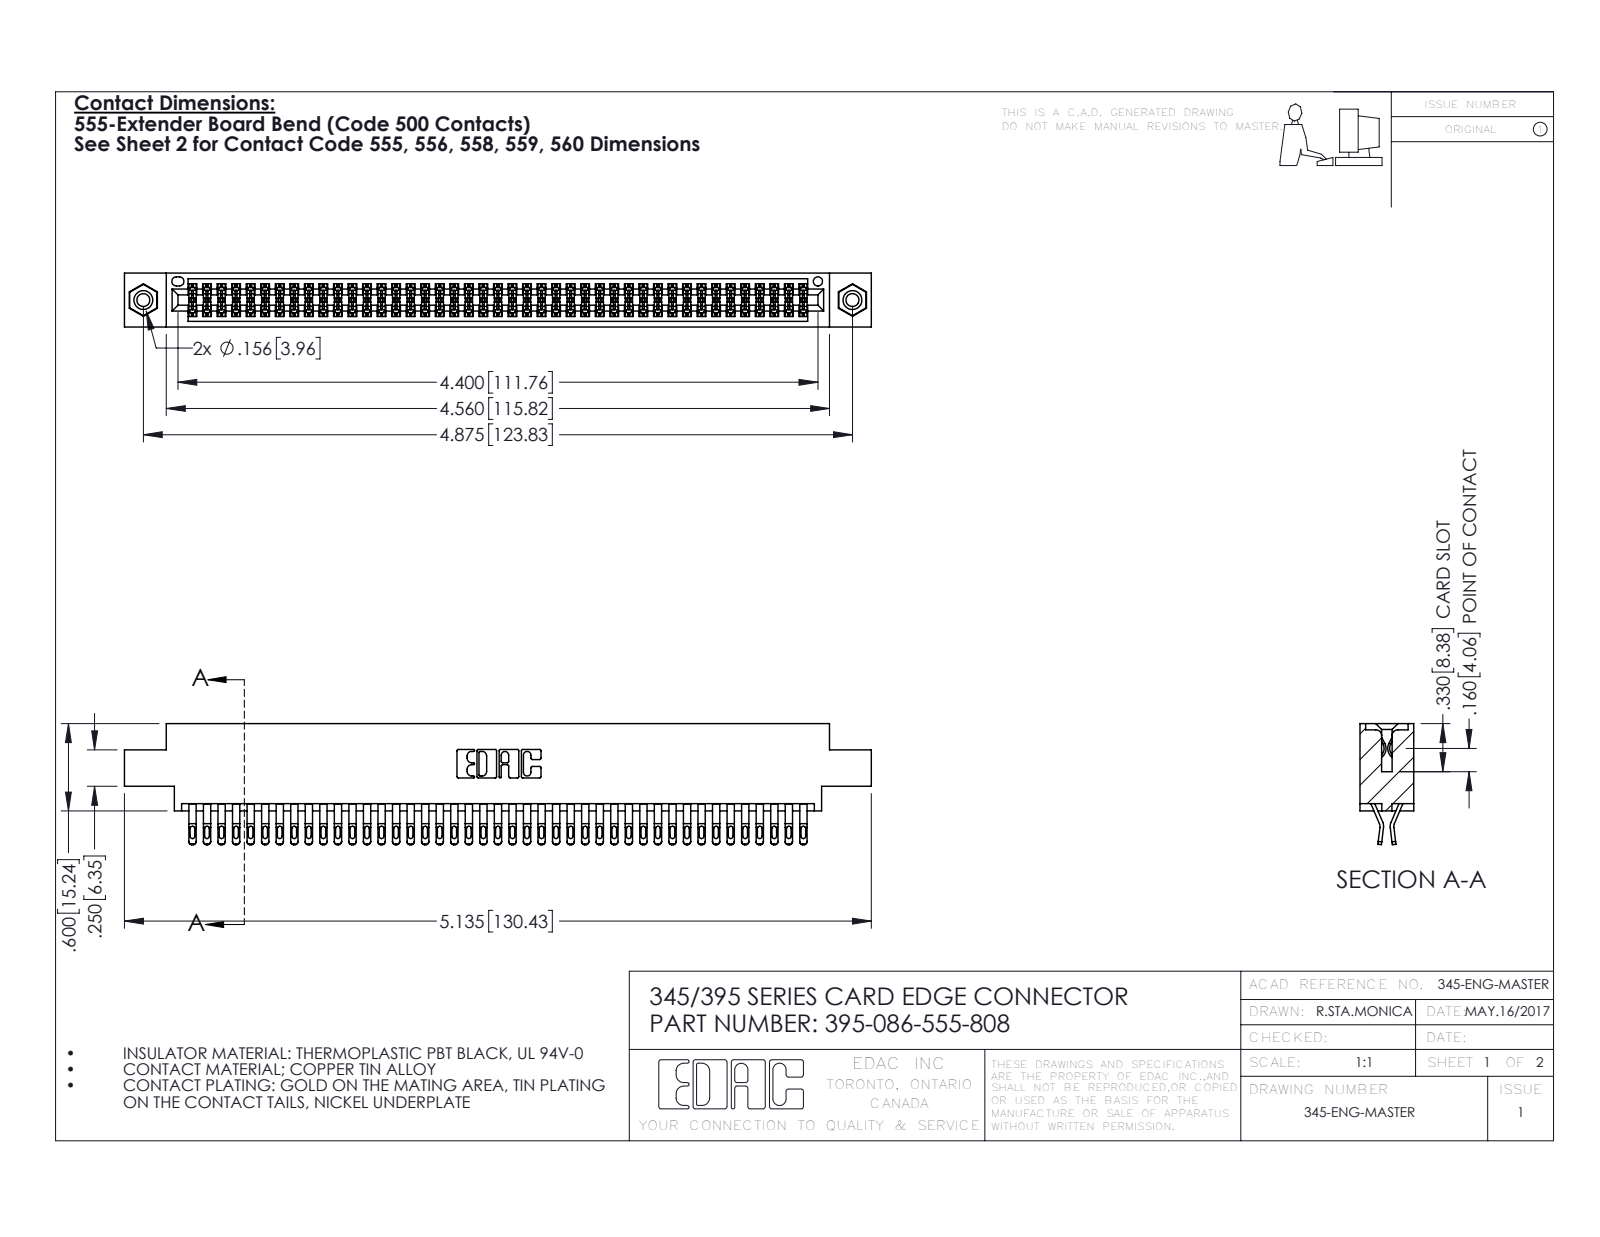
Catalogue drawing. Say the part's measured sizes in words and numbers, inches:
The part is named "395-086-555-808; 345-292-001_555 Tail; 345-250-001_345-250-003-102; 345 Part_0.170 Offset - 0.156 Dia-TI". Its 3-D file was written by "SolidWorks 2016 (CONFIG_CONTROL_DESIGN)". It is 89 solids with 5006 faces: 2782 planar, 2208 cylindrical and 16 other. Overall it measures 5.135 by 0.832 by 0.37 inches. Its volume is 0.782 cubic inches and its surface area 30.97 square inches. Round holes: 2 of diameter 0.089, 2 of diameter 0.125, 2 of diameter 0.156, 1 of diameter 0.064. Round bosses or shafts: 2 of diameter 0.155. Partial cylindrical surfaces (rounded edges, fillets, slot ends): 215 of radius 0.016, 172 of radius 0.02, 129 of radius 0.006, 22 of radius 0.01, 6 of radius 0.007, 6 of radius 0.031, 3 of radius 0.026, 2 of radius 0.01. The main face-to-face distances are 0.072, 0.298, 0.37, 0.025, 0.2, 0.098, 0.272, 0.225, 0.175, 0.149. The hole center spacings are 0.27, 4.639, 4.875.
